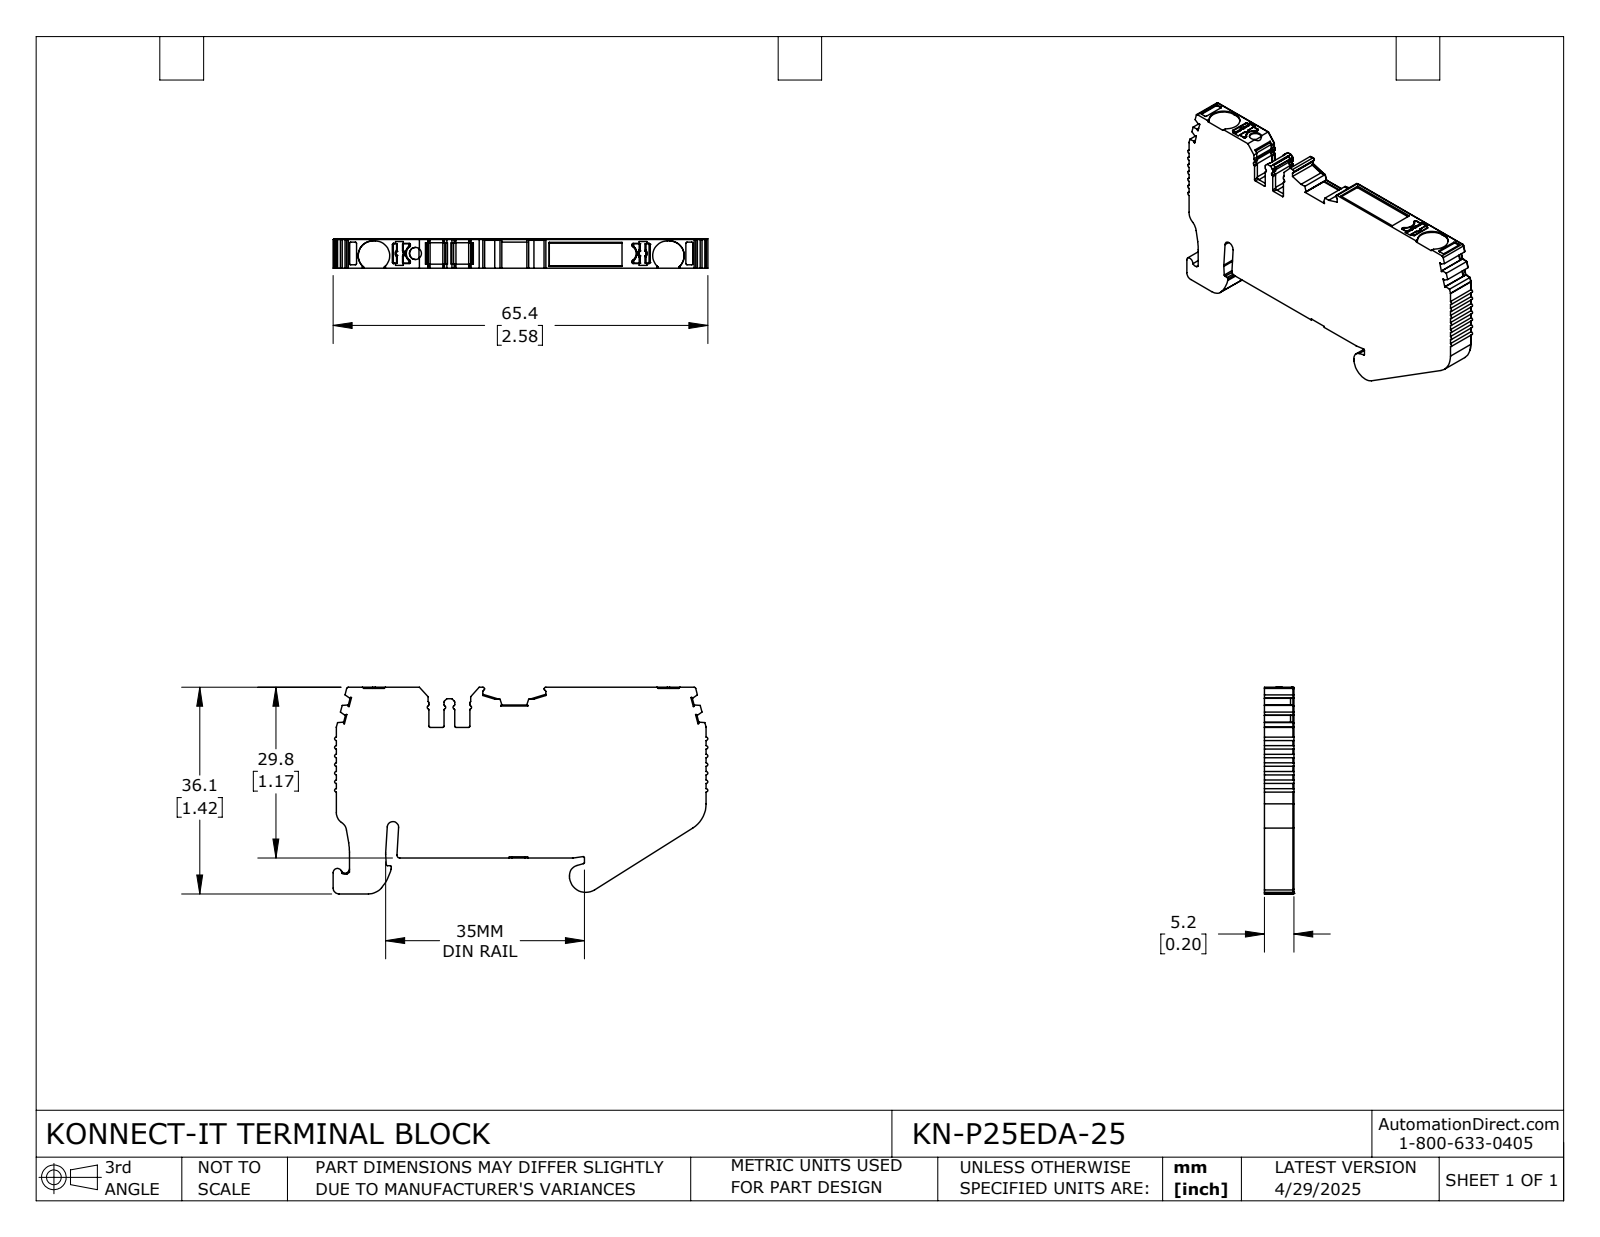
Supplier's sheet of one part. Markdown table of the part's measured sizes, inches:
| quantity | value |
| --- | --- |
| part name | KN-P25EDA-25 |
| STEP written by | SolidWorks 2024 (CONFIG_CONTROL_DESIGN) |
| units | inches |
| bodies | 1 solid, 594 faces (327 planar, 230 cylindrical, 37 other) |
| overall size | 2.576 × 1.42 × 0.203 |
| volume | 0.584 in³ |
| surface area | 7.959 in² |
| round holes (diameter × count) | 0.083 × 1 |
| partial cylindrical surfaces (radius × count) | 0.008 × 54, 0.012 × 39, 0.02 × 18, 0.004 × 17, 0.016 × 9, 0.006 × 8, 0.1 × 4, 0.039 × 3 |
| main face-to-face distances | 0.203, 1.166, 1.174, 2.543, 0.177, 0.197, 0.246, 1.412, 0.079, 1.42 |
